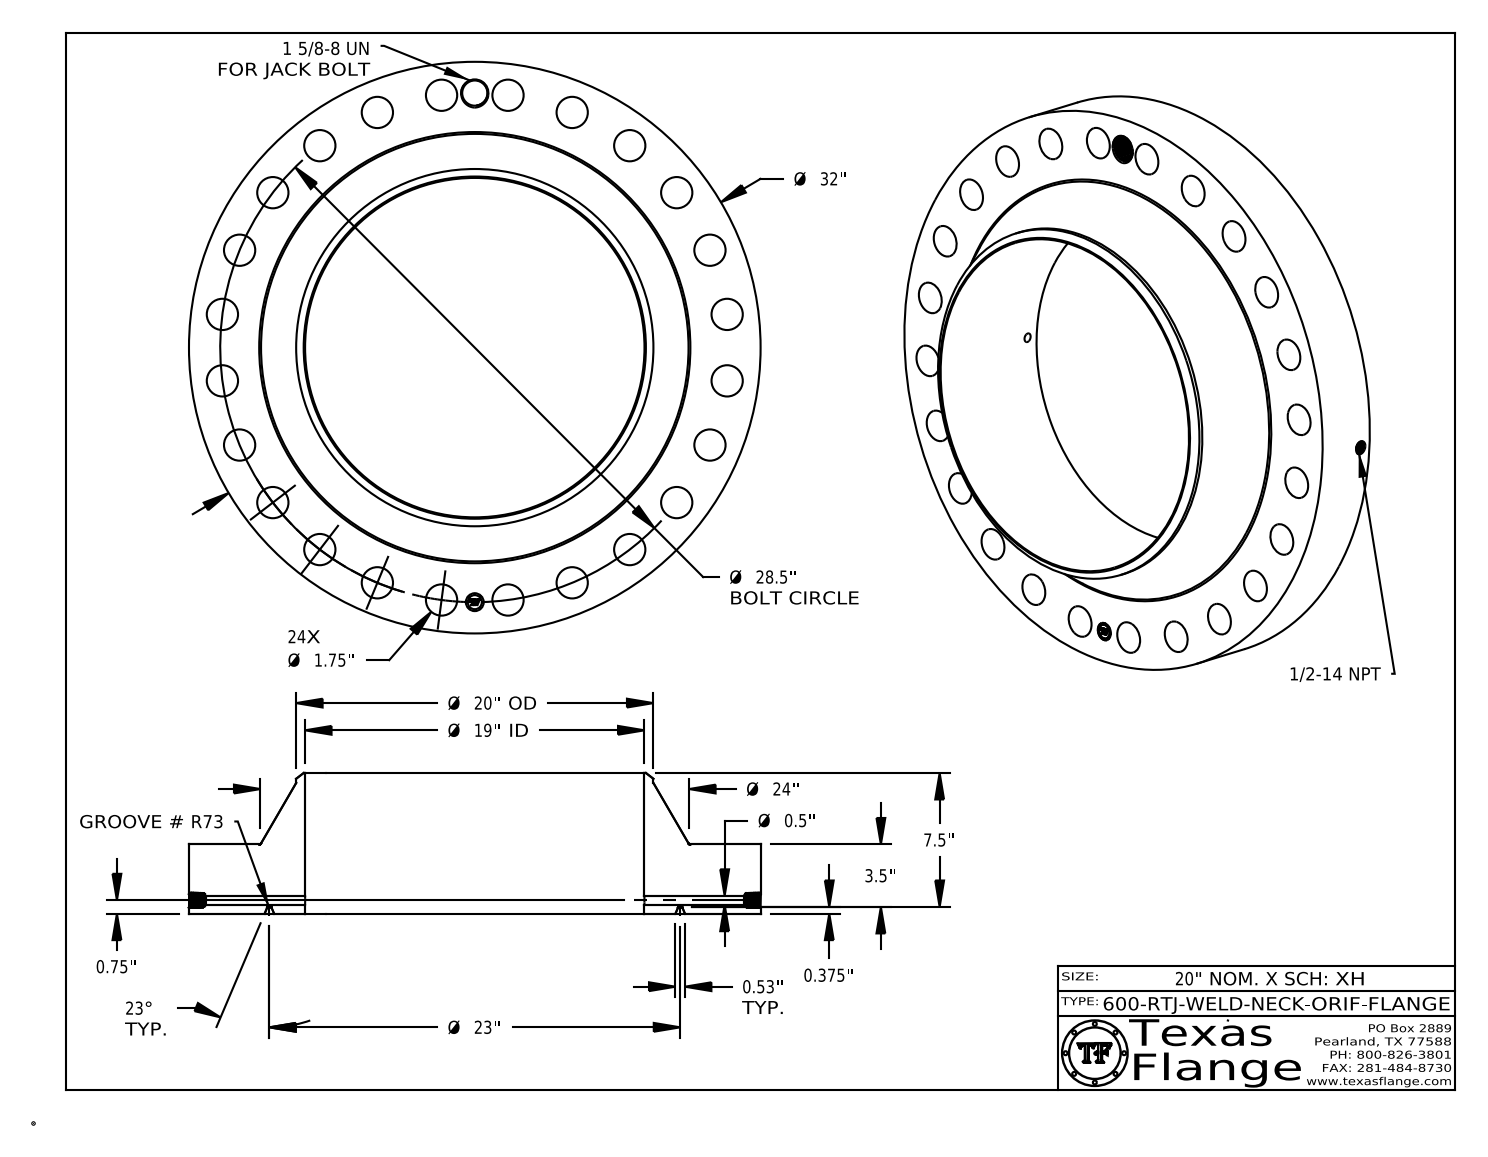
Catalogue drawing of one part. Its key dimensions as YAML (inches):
part_name: "600-RTJ-WELD-NECK"
step_written_by: "CATIA V5 STEP AP214 (AUTOMOTIVE_DESIGN)"
units: inches
bodies: {solids: 1, faces: 904, planar: 370, cylindrical: 155, other: 379}
overall_size: [32, 32, 7.875]
volume: 2123
surface_area: 2546
round_holes:
  - {diameter: 1.75, count: 24}
  - {diameter: 0.5, count: 1}
  - {diameter: 0.672, count: 1}
  - {diameter: 1, count: 1}
  - {diameter: 1.409, count: 1}
  - {diameter: 19, count: 1}
round_bosses_or_shafts:
  - {diameter: 0.061, count: 8}
  - {diameter: 32, count: 1}
  - {diameter: 20, count: 1}
  - {diameter: 0.788, count: 1}
face_to_face_distances: [3.875, 0.375, 3.5, 7.875, 7.5, 4, 0.015, 3.86, 3.485, 4.015]
hole_center_spacings: [14.25, 17.35, 24.681, 28.256, 10.906, 3.72, 7.376, 20.152]
